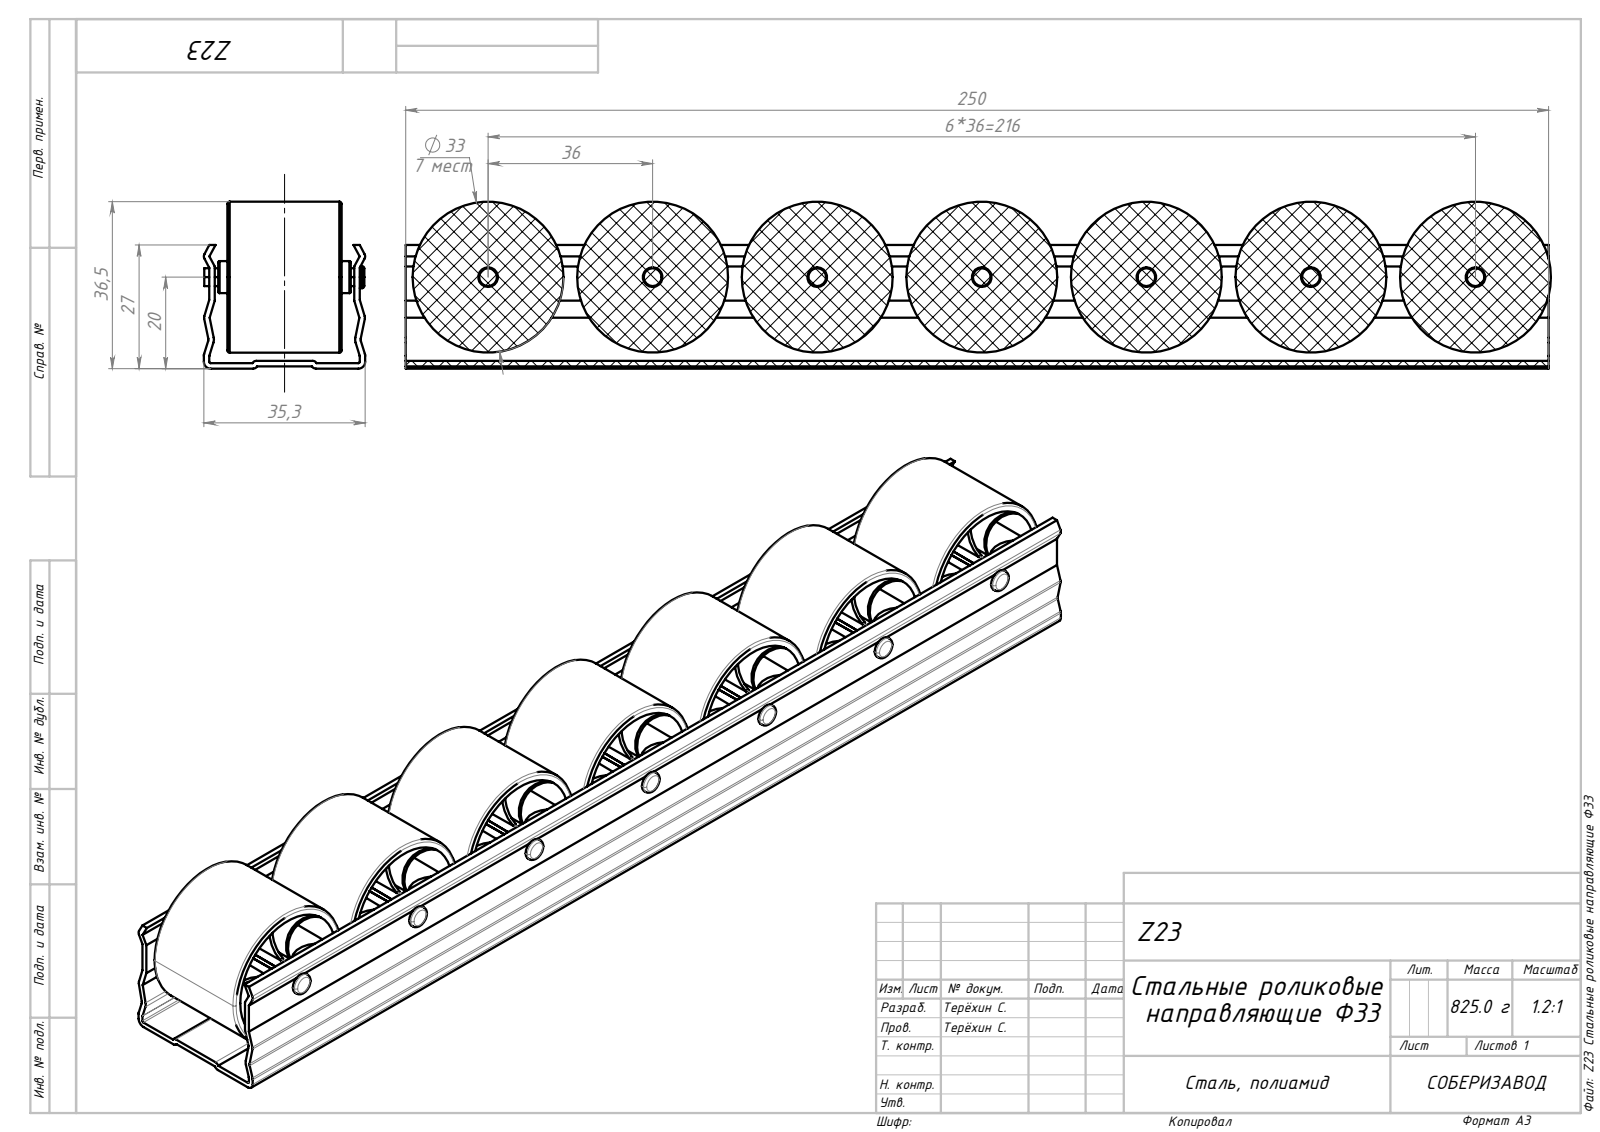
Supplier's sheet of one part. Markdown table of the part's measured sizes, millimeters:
| quantity | value |
| --- | --- |
| part name | Z23 Стальные роликовые направляющие Ф33 |
| STEP written by | SolidWorks 2022 (AUTOMOTIVE_DESIGN) |
| units | millimeters |
| bodies | 15 solids, 818 faces (430 planar, 290 cylindrical, 98 other) |
| overall size | 250.5 × 36.5 × 35.3 |
| volume | 78 733 mm³ |
| surface area | 118 439 mm² |
| round holes (diameter × count) | 2.5 × 7, 3.6 × 7, 4.3 × 7, 29.4 × 7 |
| round bosses / shafts (diameter × count) | 33 × 7, 7 × 7, 4.8 × 7, 3.9 × 7 |
| partial cylindrical surfaces (radius × count) | 6 × 88, 1 × 10, 0.3 × 4, 1.5 × 4, 2.2 × 2 |
| main face-to-face distances | 1.2, 1.02, 25.45, 0.5, 36, 50.9, 16.95, 15.95, 1, 31.7 |
| hole center spacings | 36, 72, 108, 144, 180, 216 |
